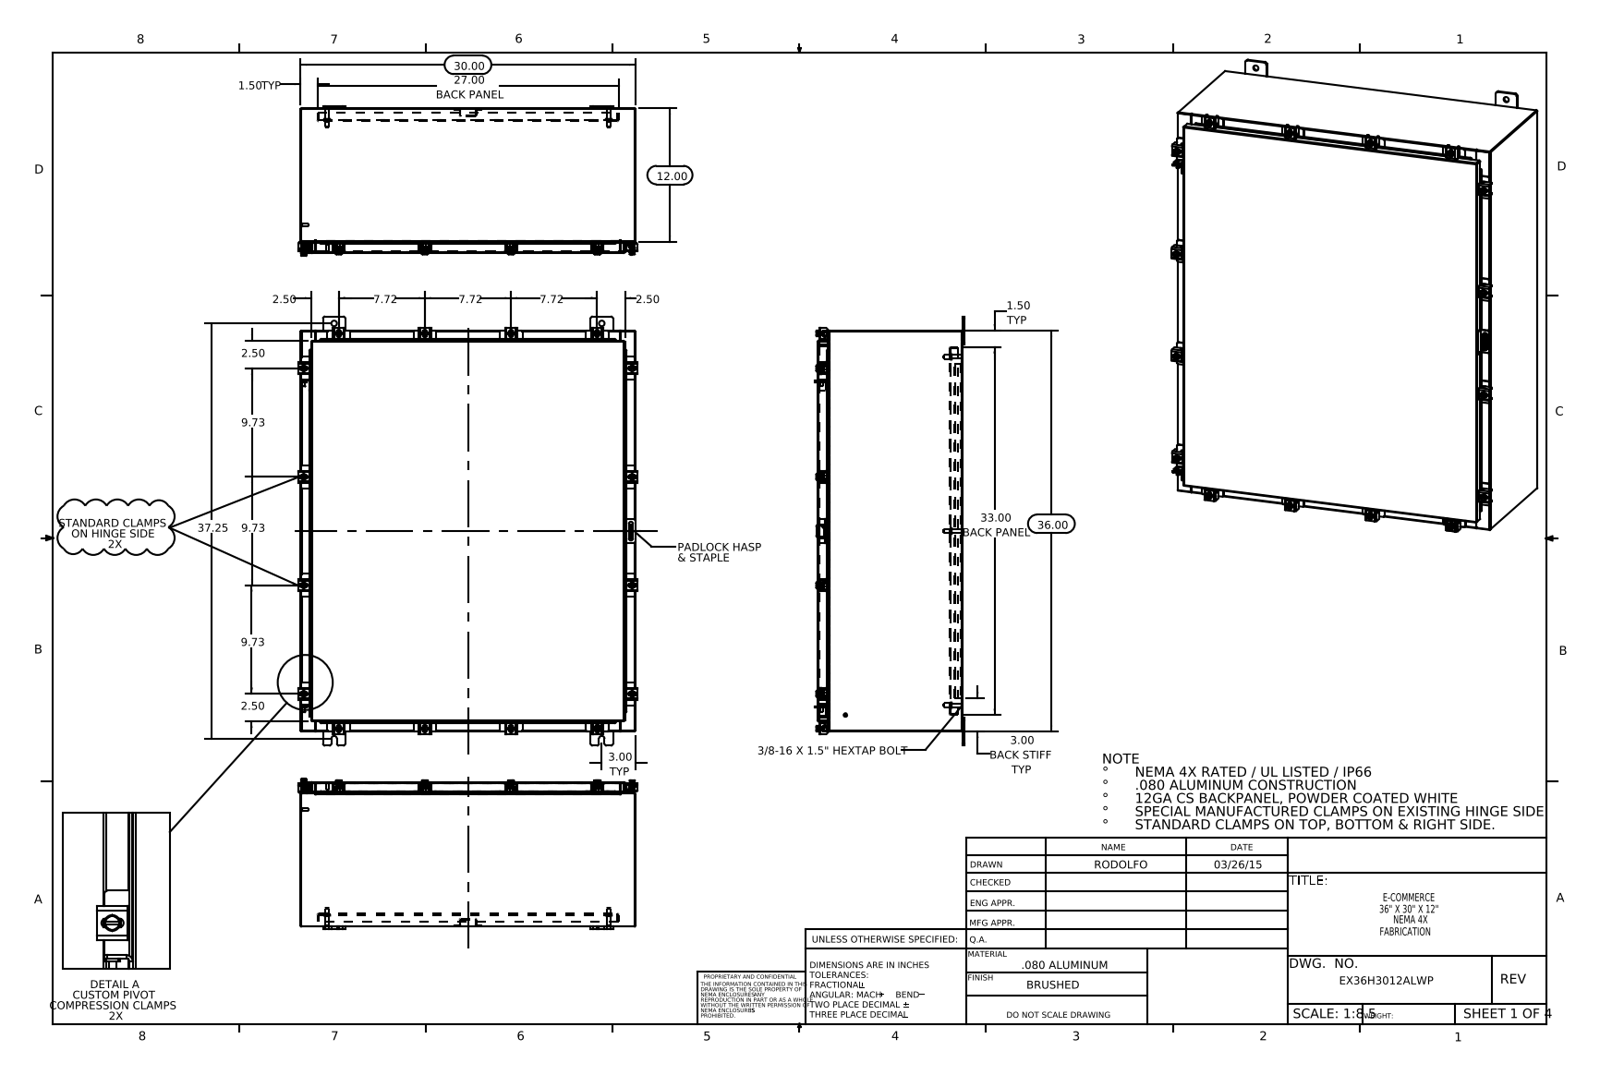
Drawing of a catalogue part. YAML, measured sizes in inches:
part_name: "Quarter-20 CD Stud; EX36H3012ALWP Backpanel; EX36H3012ALWP Special Clamp; EX36H3012ALWP Top (+8 more)"
step_written_by: "SolidWorks 2014 (CONFIG_CONTROL_DESIGN)"
units: inches
bodies: {solids: 109, faces: 2711, planar: 1431, cylindrical: 1060, other: 220}
overall_size: [38.5, 30.421, 13.453]
volume: 421.1
surface_area: 10507
round_holes:
  - {diameter: 0.213, count: 17}
  - {diameter: 0.26, count: 17}
  - {diameter: 0.5, count: 10}
  - {diameter: 0.125, count: 1}
  - {diameter: 0.25, count: 1}
round_bosses_or_shafts:
  - {diameter: 0.5, count: 17}
  - {diameter: 0.25, count: 17}
  - {diameter: 0.399, count: 15}
  - {diameter: 0.625, count: 6}
  - {diameter: 0.375, count: 6}
  - {diameter: 0.33, count: 6}
  - {diameter: 0.315, count: 2}
  - {diameter: 0.236, count: 2}
partial_cylinders:
  - {radius: 0.06, count: 74}
  - {radius: 0.141, count: 34}
  - {radius: 0.12, count: 32}
  - {radius: 0.013, count: 30}
  - {radius: 0.088, count: 26}
  - {radius: 0.09, count: 24}
  - {radius: 0.19, count: 24}
  - {radius: 0.05, count: 23}
face_to_face_distances: [0.075, 12.9, 12.826, 12.975, 0.104, 1, 1.075, 11.826, 11.9, 1.179]
hole_center_spacings: [31.017, 35.451, 2.347, 4.44, 5.299, 9.73, 10.964, 13.241]
